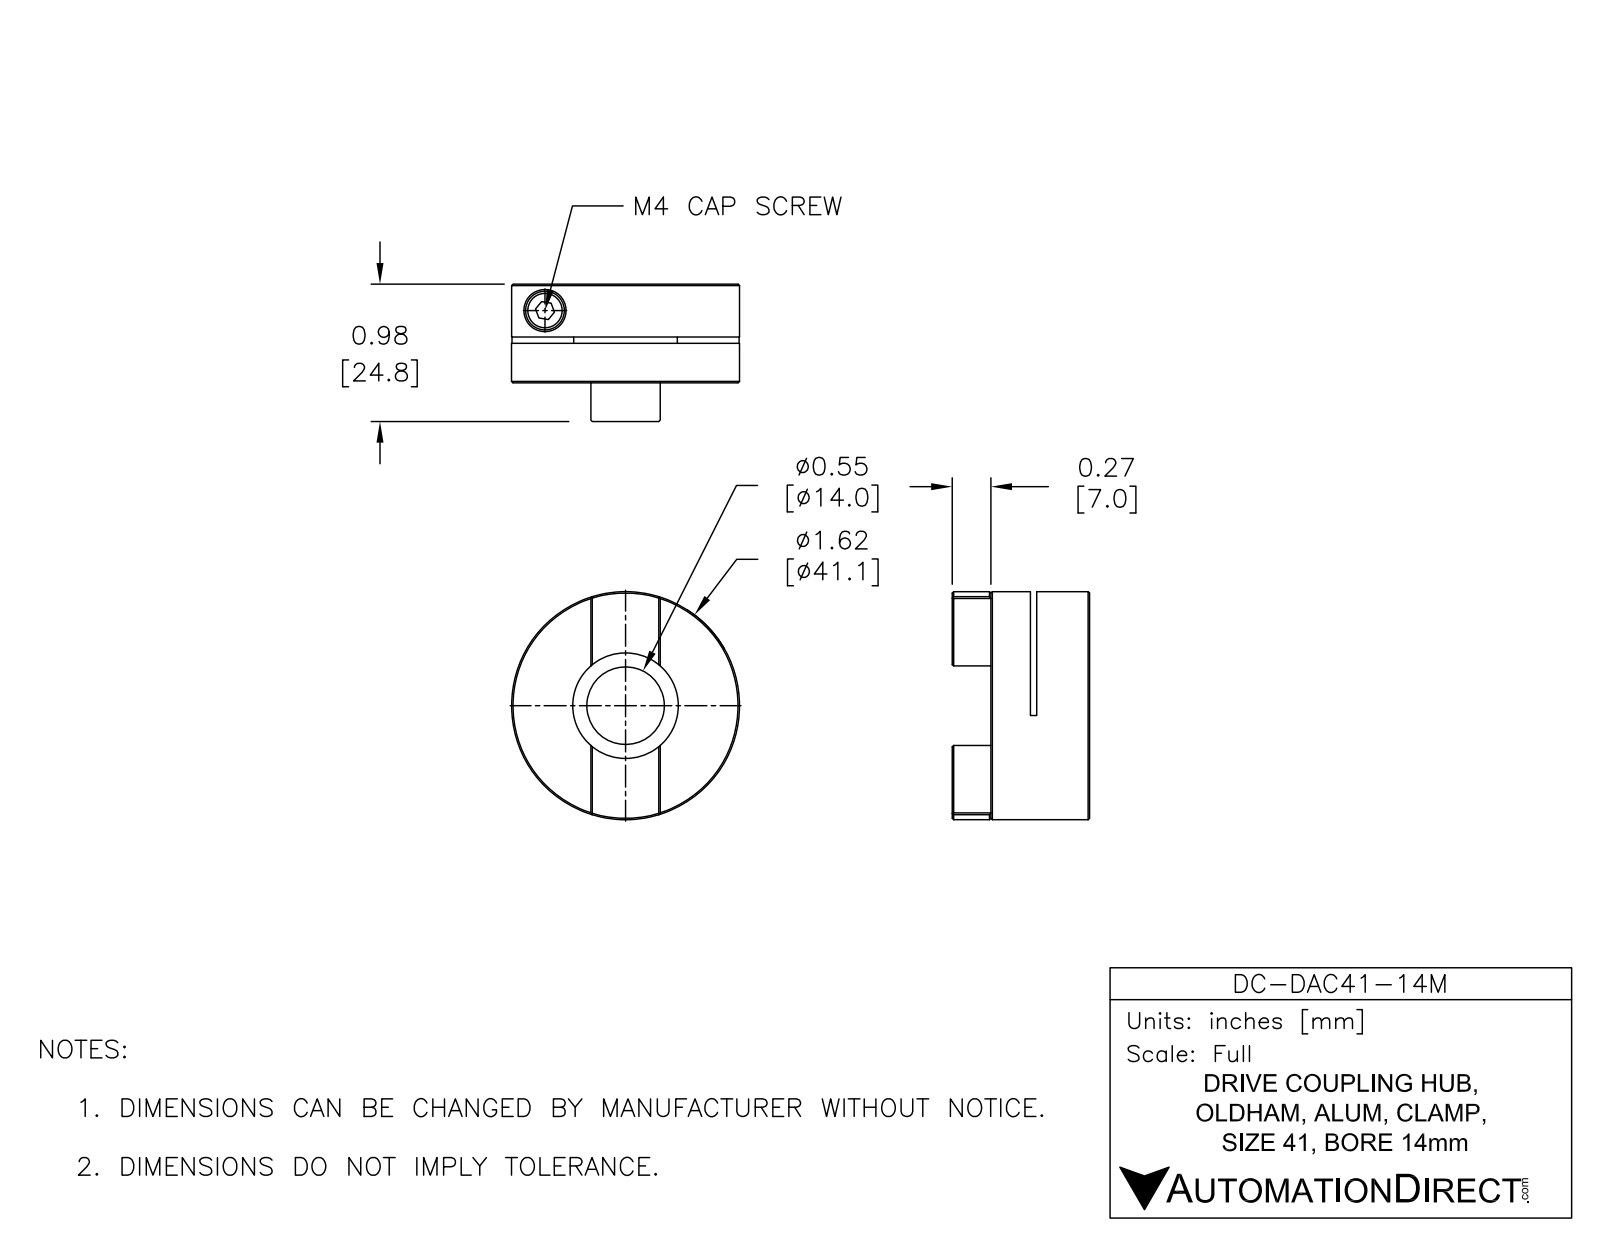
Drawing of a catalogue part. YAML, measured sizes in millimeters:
part_name: "DC-DAC41-14M"
step_written_by: "SolidWorks 2015 (AUTOMOTIVE_DESIGN)"
units: millimeters
bodies: {solids: 1, faces: 51, planar: 24, cylindrical: 15, other: 12}
overall_size: [41.15, 41.15, 24.78]
volume: 22337
surface_area: 6912
round_holes:
  - {diameter: 3.99, count: 1}
  - {diameter: 7.62, count: 1}
  - {diameter: 14, count: 1}
  - {diameter: 15.87, count: 1}
round_bosses_or_shafts:
  - {diameter: 41.15, count: 1}
partial_cylinders:
  - {radius: 22.23, count: 1}
face_to_face_distances: [17.8, 6.97, 24.77, 12.52, 1.17, 1.22, 2.39, 7.03, 17.74, 4.22]
